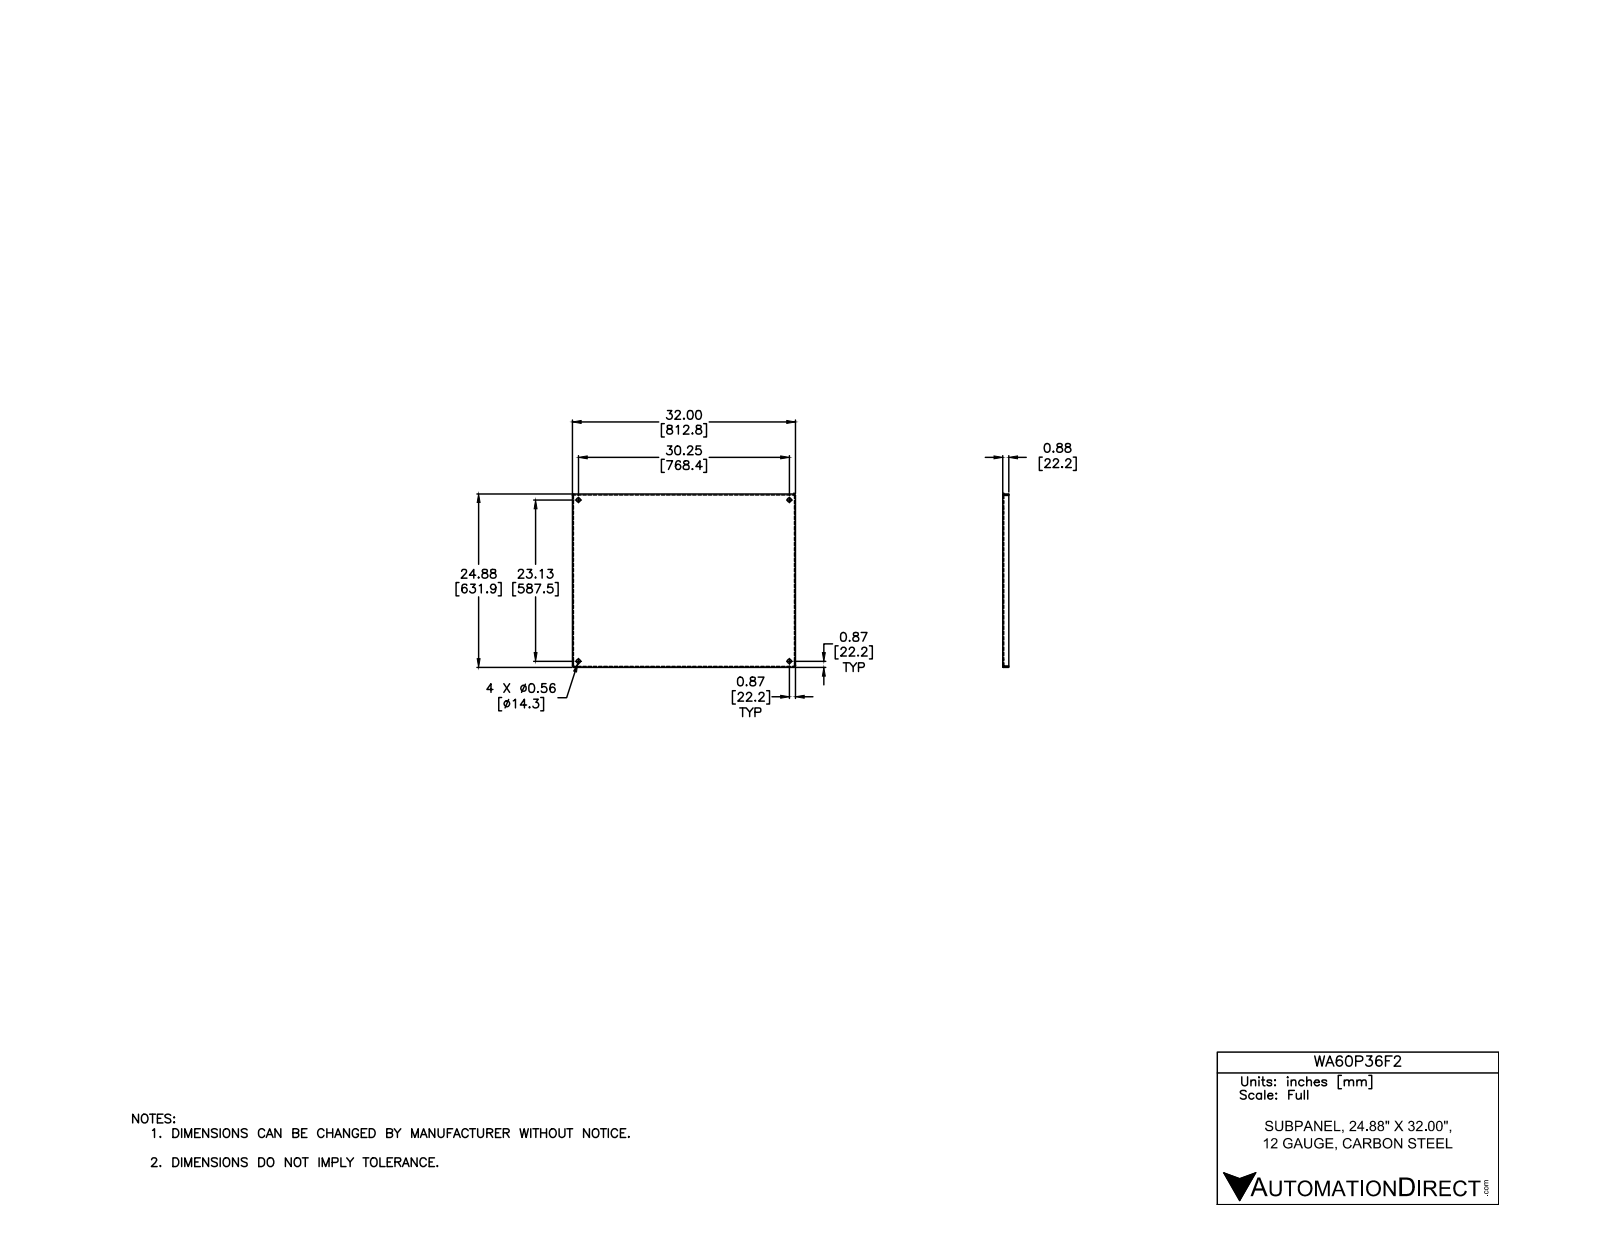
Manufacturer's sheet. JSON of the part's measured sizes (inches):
{"part_name": "WA_P_F", "step_written_by": "Autodesk Inventor 2012 (AUTOMOTIVE_DESIGN)", "units": "inches", "bodies": {"solids": 1, "faces": 42, "planar": 22, "cylindrical": 12, "other": 8}, "overall_size": [32, 24.88, 0.875], "volume_in3": 82.42, "surface_area_in2": 1770, "round_holes": [[0.563, 4]], "partial_cylinders_radius": [[0.031, 4], [0.125, 4]], "face_to_face_distances": [0.094, 24.786, 31.906, 24.88, 24.693, 32, 31.813, 0.781, 0.875, 0.16], "hole_center_spacings": [23.13, 30.25, 30.25, 38.08, 38.08]}
